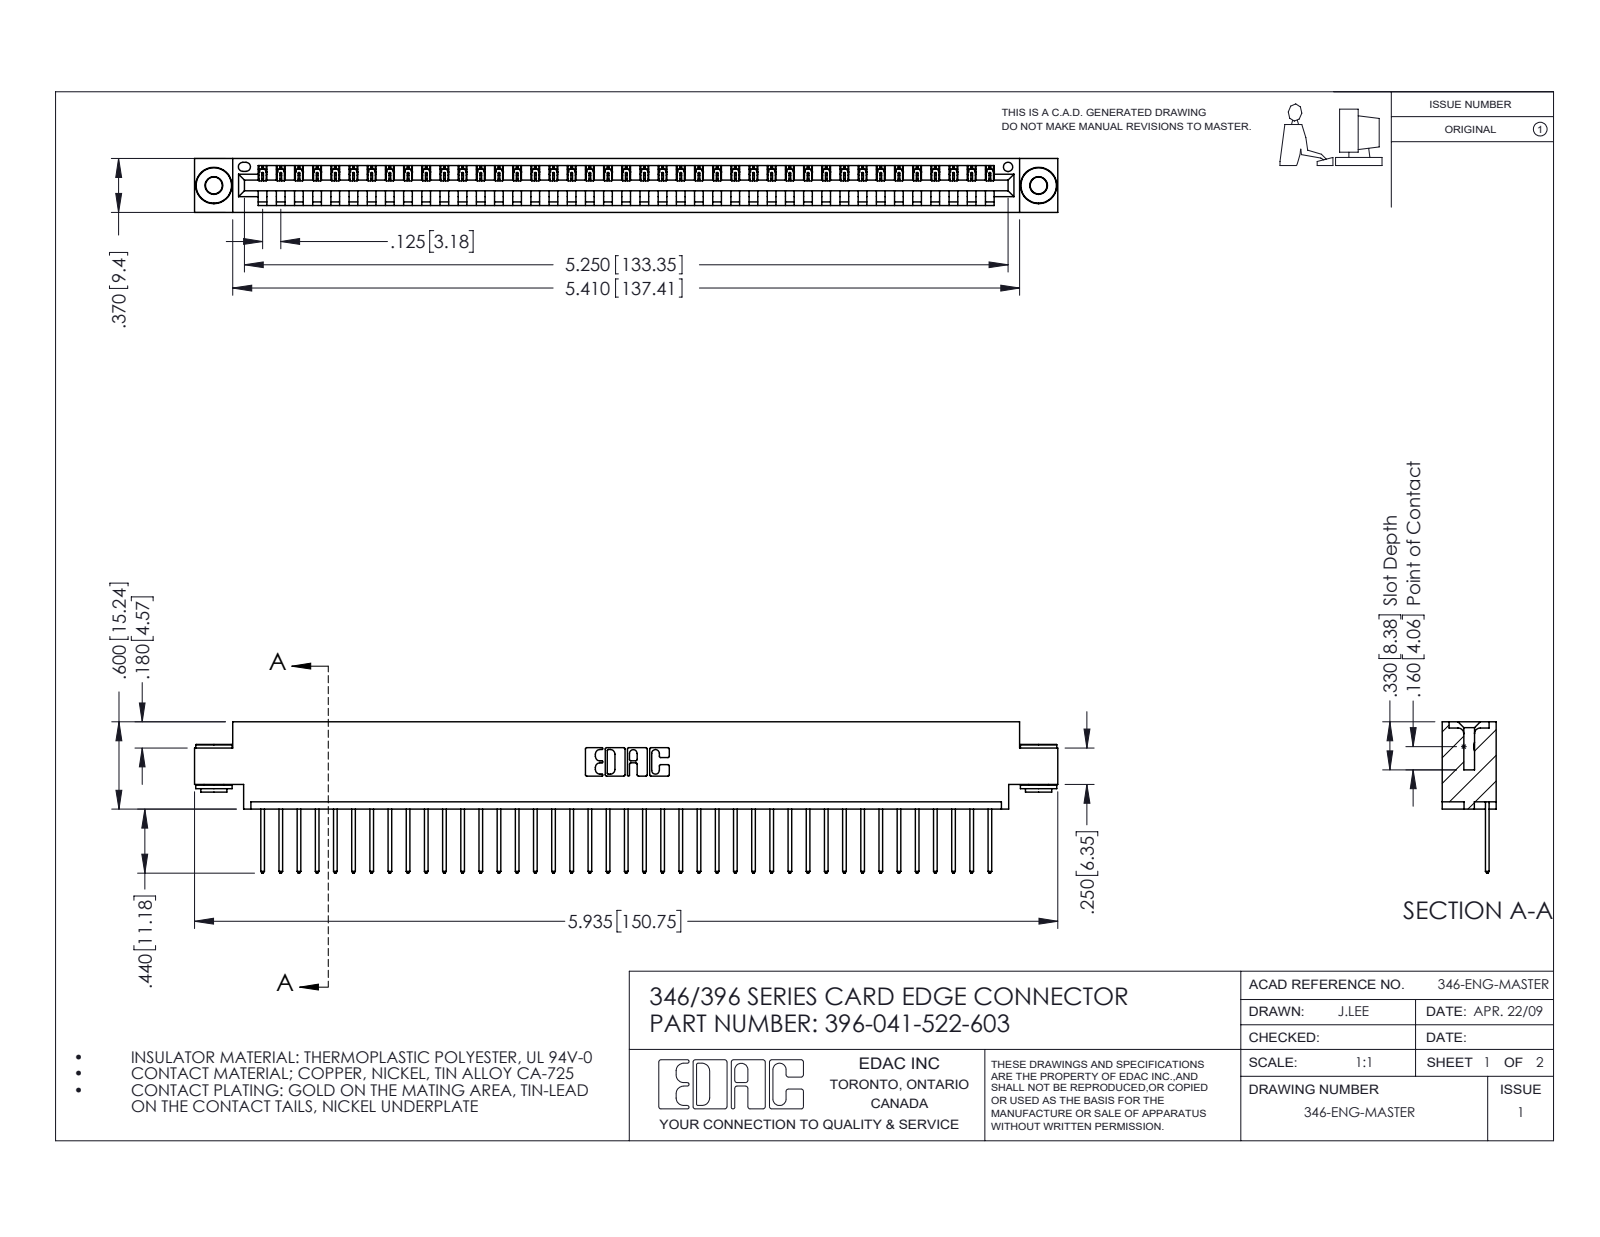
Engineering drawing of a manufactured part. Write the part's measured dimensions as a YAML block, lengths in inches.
part_name: "345-250-002_345-250-002-102; 346 Part_0.170 Offset - 0.156 Dia-TH; 345-292-001_345-293-122; 396-041-522-603"
step_written_by: "SolidWorks 2016 (CONFIG_CONTROL_DESIGN)"
units: inches
bodies: {solids: 44, faces: 2542, planar: 1730, cylindrical: 804, other: 8}
overall_size: [5.935, 1.04, 0.37]
volume: 0.872
surface_area: 28.5
round_holes:
  - {diameter: 0.116, count: 2}
  - {diameter: 0.156, count: 2}
  - {diameter: 0.064, count: 1}
round_bosses_or_shafts:
  - {diameter: 0.25, count: 2}
  - {diameter: 0.18, count: 2}
  - {diameter: 0.136, count: 2}
partial_cylinders:
  - {radius: 0.006, count: 82}
  - {radius: 0.01, count: 82}
  - {radius: 0.01, count: 22}
  - {radius: 0.007, count: 6}
  - {radius: 0.031, count: 6}
  - {radius: 0.026, count: 3}
  - {radius: 0.031, count: 2}
  - {radius: 0.04, count: 2}
face_to_face_distances: [0.048, 0.322, 0.37, 0.25, 0.025, 0.072, 0.298, 0.148, 0.222, 0.1]
hole_center_spacings: [0.246, 5.461, 5.67]
